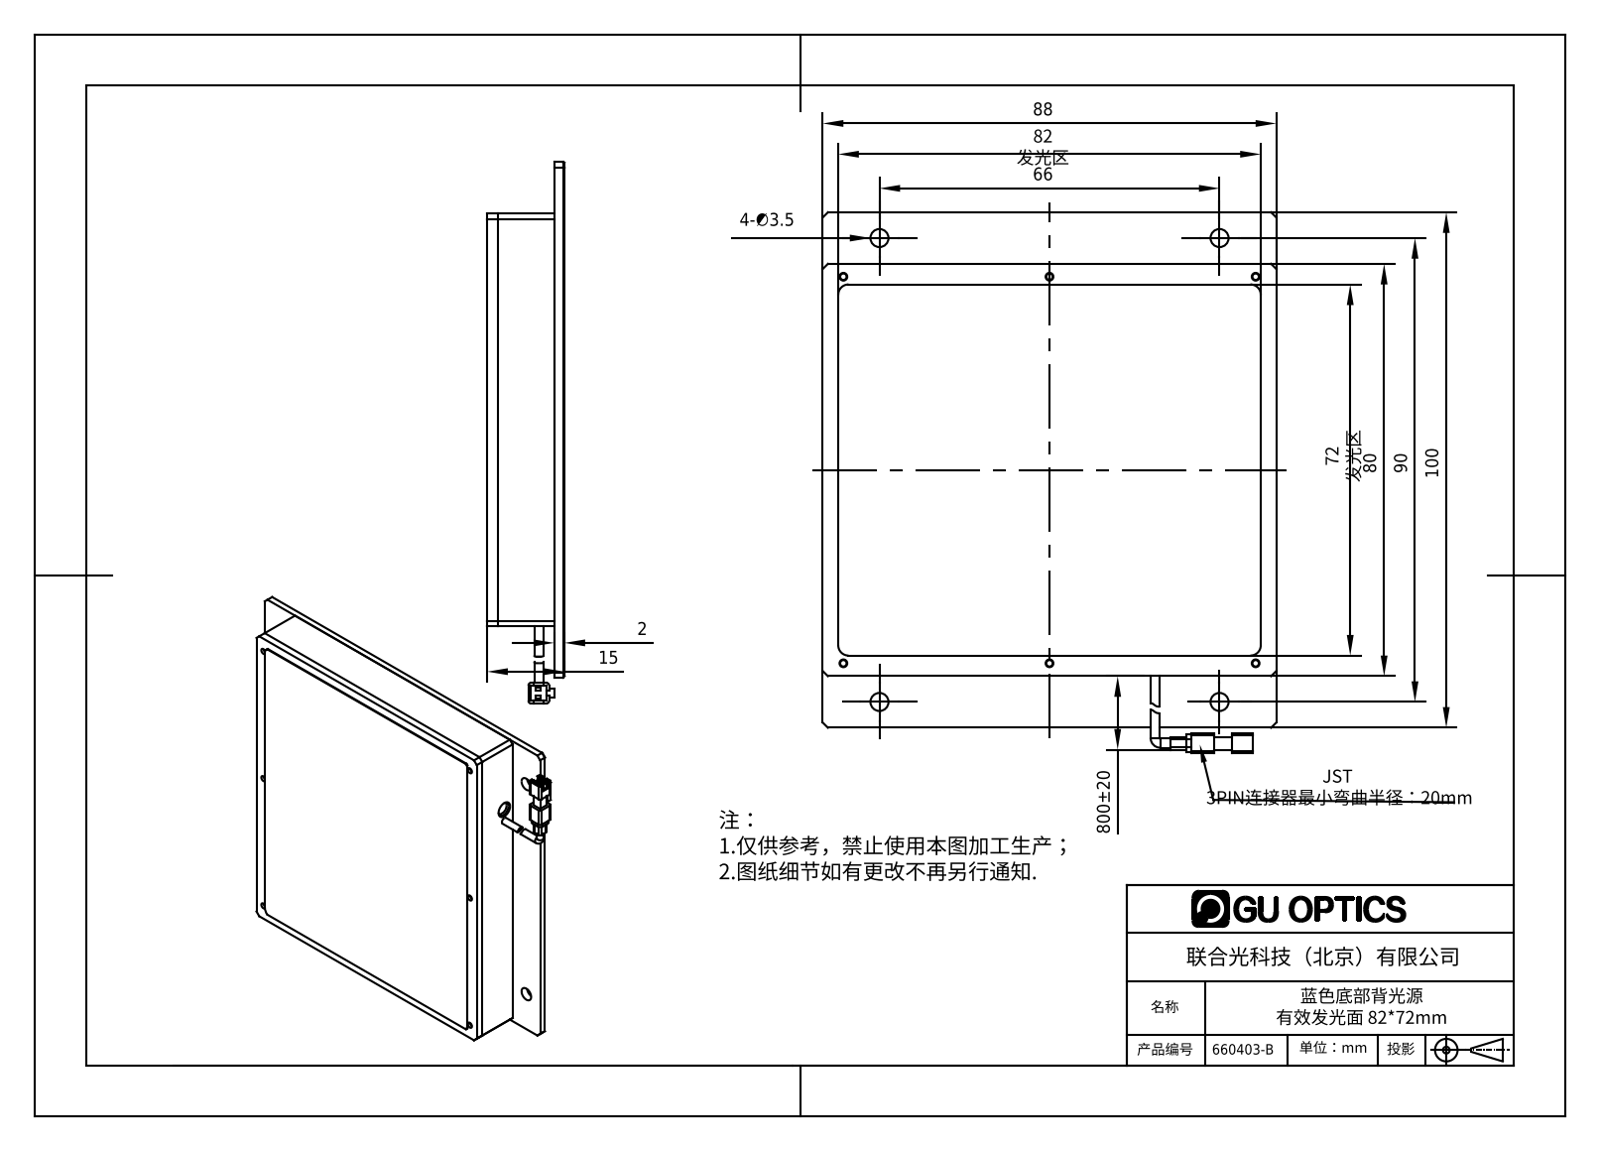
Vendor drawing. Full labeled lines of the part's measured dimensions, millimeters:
Part name (STEP PRODUCT): 660403-B
STEP written by: SolidWorks 2016 (AUTOMOTIVE_DESIGN)
Units: millimetres
Bodies: 5 solids, 421 faces (188 planar, 134 cylindrical, 99 other)
Overall size (bounding box): 105 × 88 × 15.2
Volume: 44 726 mm³ · Surface area: 43 208 mm²
Round holes (diameter × count): ⌀1.25 ×12, ⌀1.6 ×12, ⌀1.5 ×6, ⌀2.4 ×6, ⌀2.8 ×6, ⌀3.5 ×4, ⌀3.6 ×1
Round bosses / shafts (diameter × count): ⌀1.75 ×2
Partial cylindrical surfaces — rounded edges, fillets, slot ends (radius × count): R0.5 ×8, R1 ×8, R2 ×4, R1.5 ×2, R0.65 ×1, R0.65 ×1, R1.71 ×1, R1.98 ×1
Main face-to-face distances: 2, 13, 11, 2.2, 15.2, 13.2, 3, 4, 76, 85
Hole centre spacings: 40, 80, 85.44, 0.5, 75.5, 9.9, 10.26, 33.73
